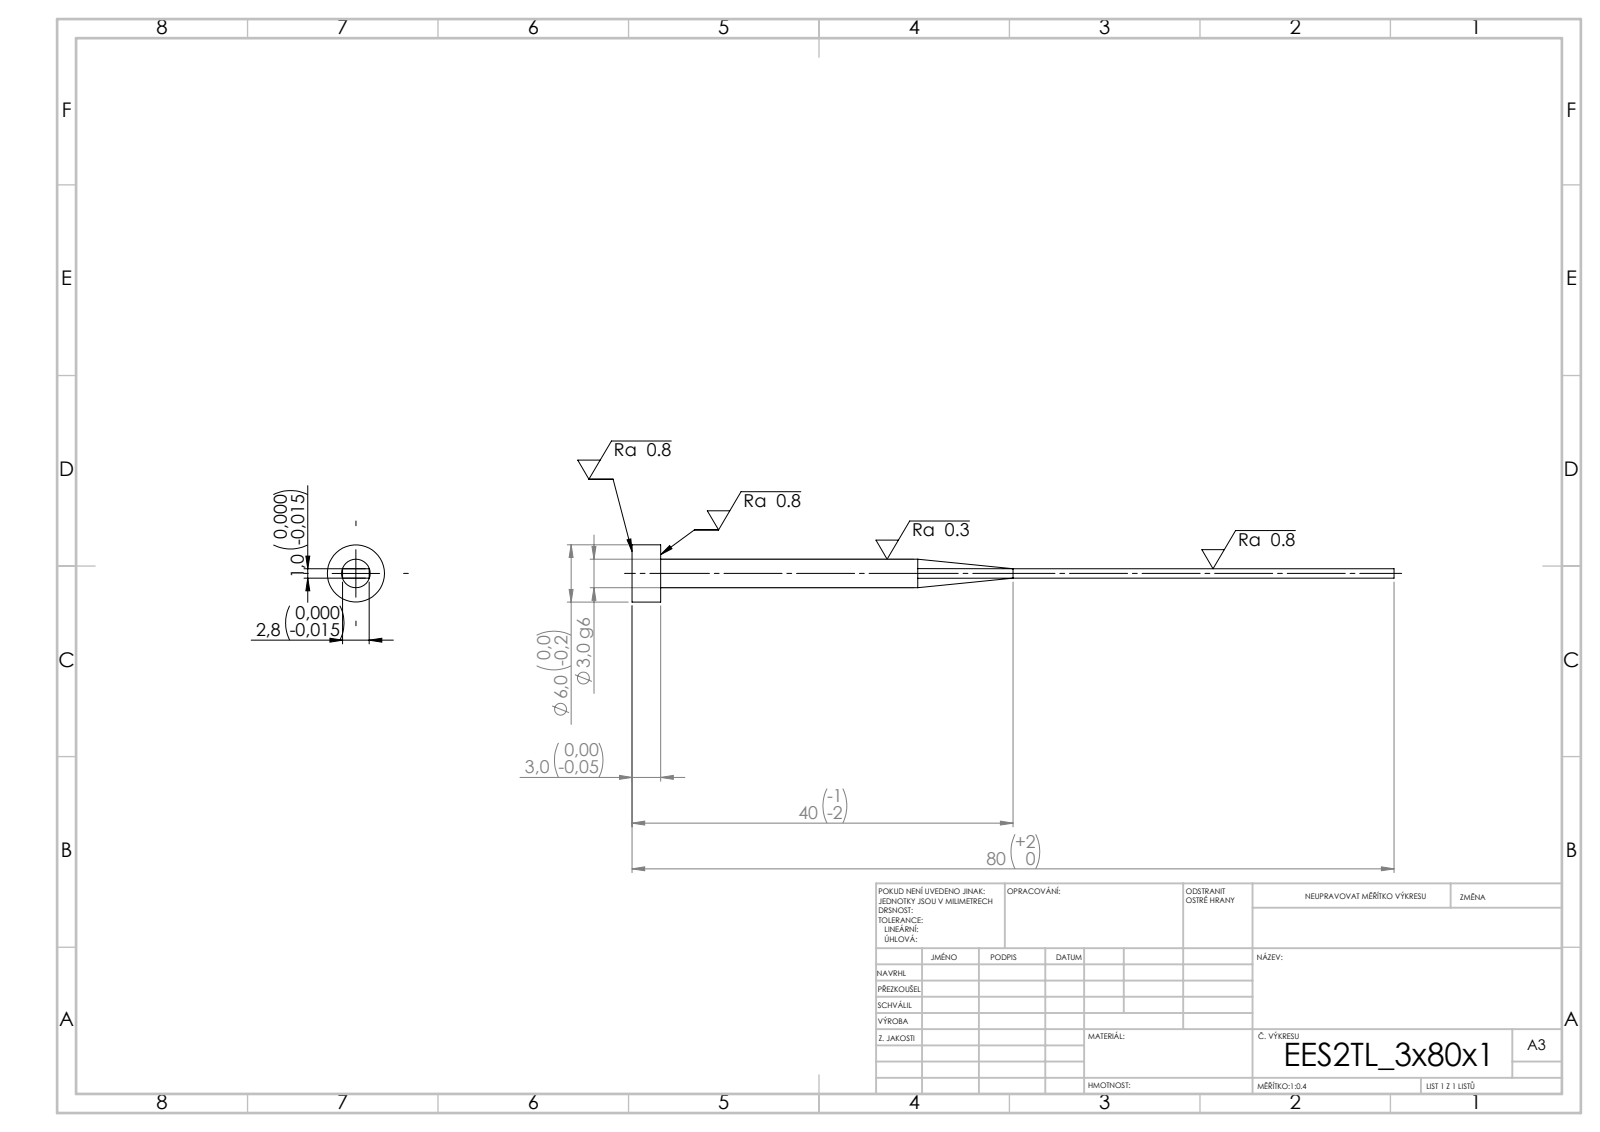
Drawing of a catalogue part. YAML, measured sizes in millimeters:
step_written_by: "SolidWorks 2019 (CONFIG_CONTROL_DESIGN)"
units: millimeters
bodies: {solids: 1, faces: 15, planar: 7, cylindrical: 4, other: 4}
overall_size: [80, 6, 6]
volume: 436
surface_area: 750
round_bosses_or_shafts:
  - {diameter: 6, count: 1}
  - {diameter: 3, count: 1}
face_to_face_distances: [1, 2.8, 3, 80, 77]
